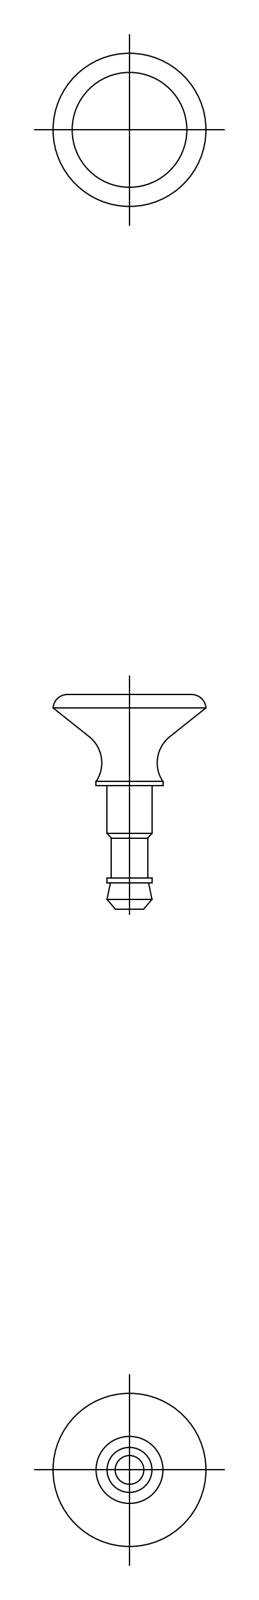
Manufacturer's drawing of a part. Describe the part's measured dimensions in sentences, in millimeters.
The part is named "plunger". Its 3-D file was written by "CADfix (AUTOMOTIVE_DESIGN)". It is 1 solid with 26 faces: 0 planar, 0 cylindrical and 26 other. Overall it measures 22.4 by 16 by 16 millimeters. Its volume is 863 cubic millimeters and its surface area 771 square millimeters.
